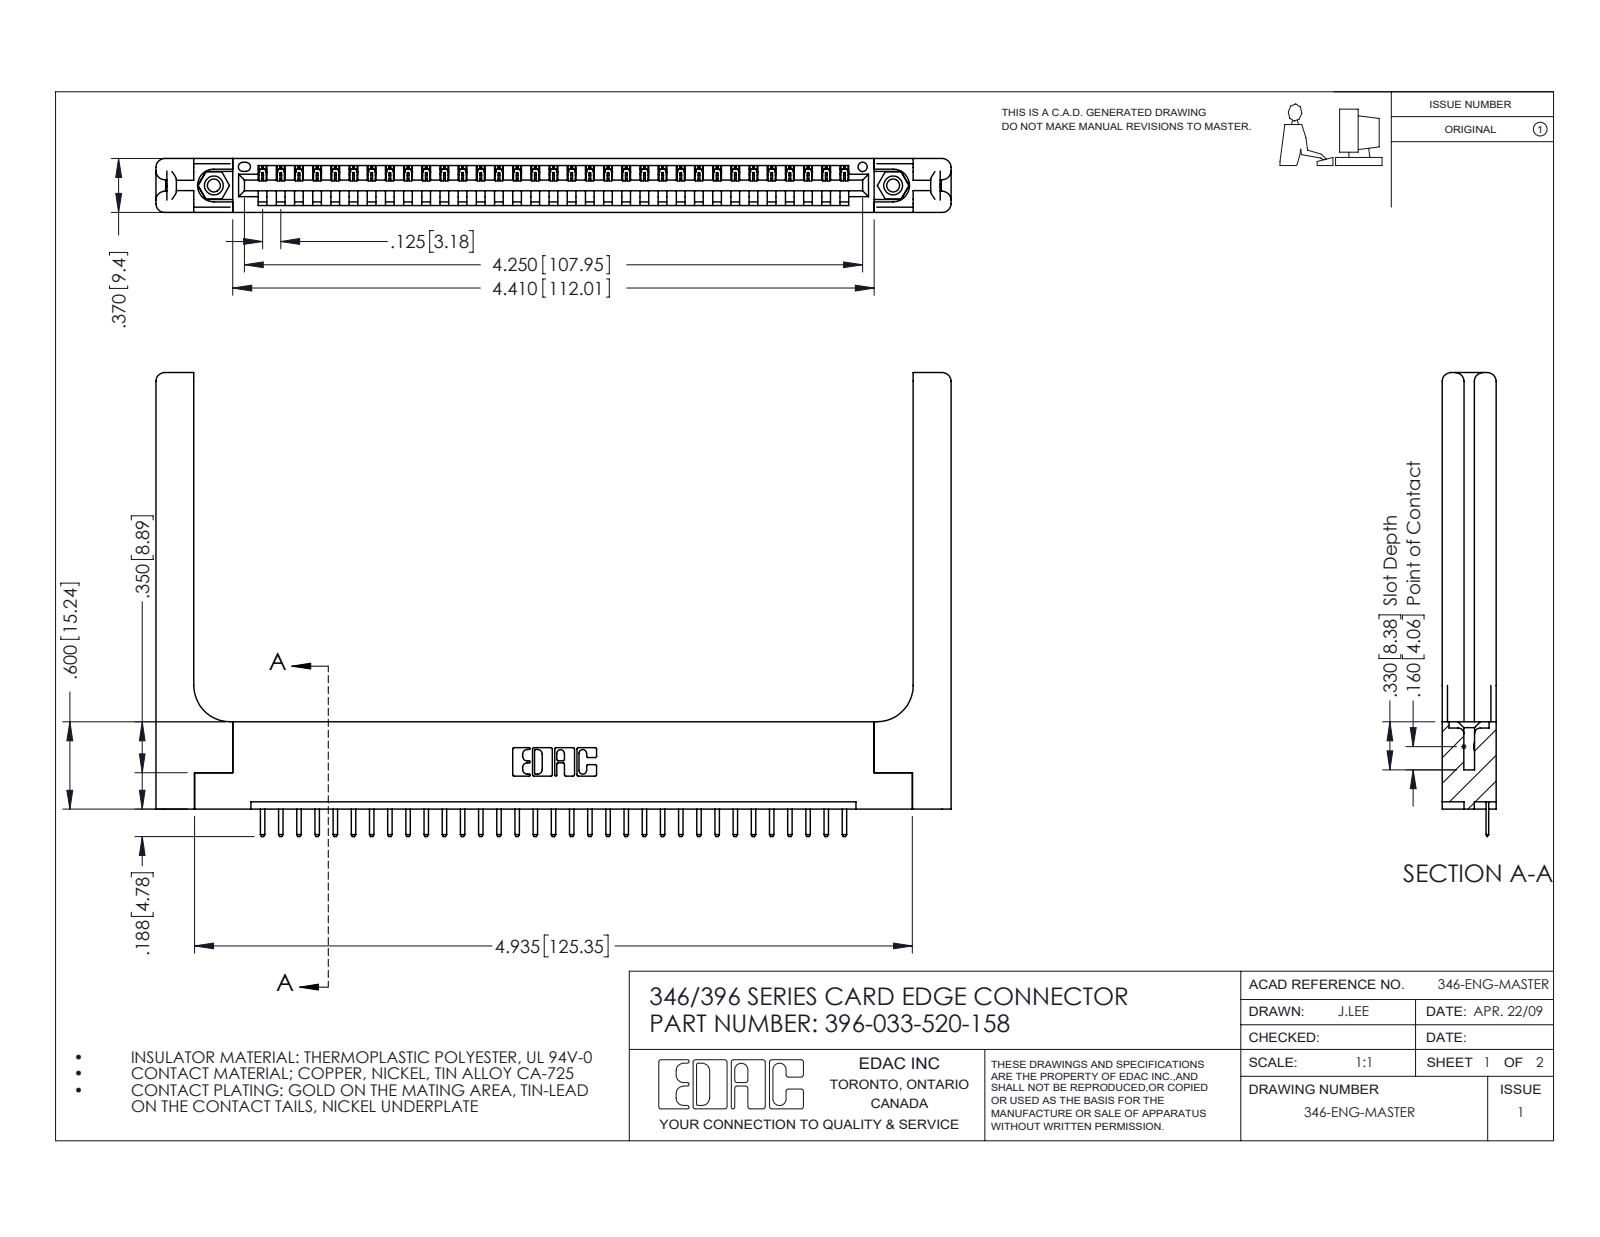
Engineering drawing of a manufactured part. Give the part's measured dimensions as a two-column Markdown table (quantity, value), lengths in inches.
| quantity | value |
| --- | --- |
| part name | 396-033-520-158; 346-220-058_345-220-058; 346 Part_Flush Mounting Lugs - 0.156 Dia-TH; 345-292-001_345-293-120 (+1 more) |
| STEP written by | SolidWorks 2016 (CONFIG_CONTROL_DESIGN) |
| units | inches |
| bodies | 38 solids, 2424 faces (1610 planar, 754 cylindrical, 60 other) |
| overall size | 5.466 × 3.188 × 0.37 |
| volume | 1.26 in³ |
| surface area | 32.81 in² |
| round holes (diameter × count) | 0.089 × 2, 0.125 × 2, 0.156 × 2, 0.064 × 1 |
| round bosses / shafts (diameter × count) | 0.155 × 2 |
| partial cylindrical surfaces (radius × count) | 0.01 × 68, 0.006 × 66, 0.01 × 22, 0.06 × 16, 0.007 × 6, 0.031 × 6, 0.026 × 3, 0.03 × 2 |
| main face-to-face distances | 0.37, 0.048, 0.322, 0.072, 0.148, 0.15, 0.25, 0.298, 0.025, 0.222 |
| hole center spacings | 0.246, 4.462, 4.67 |
